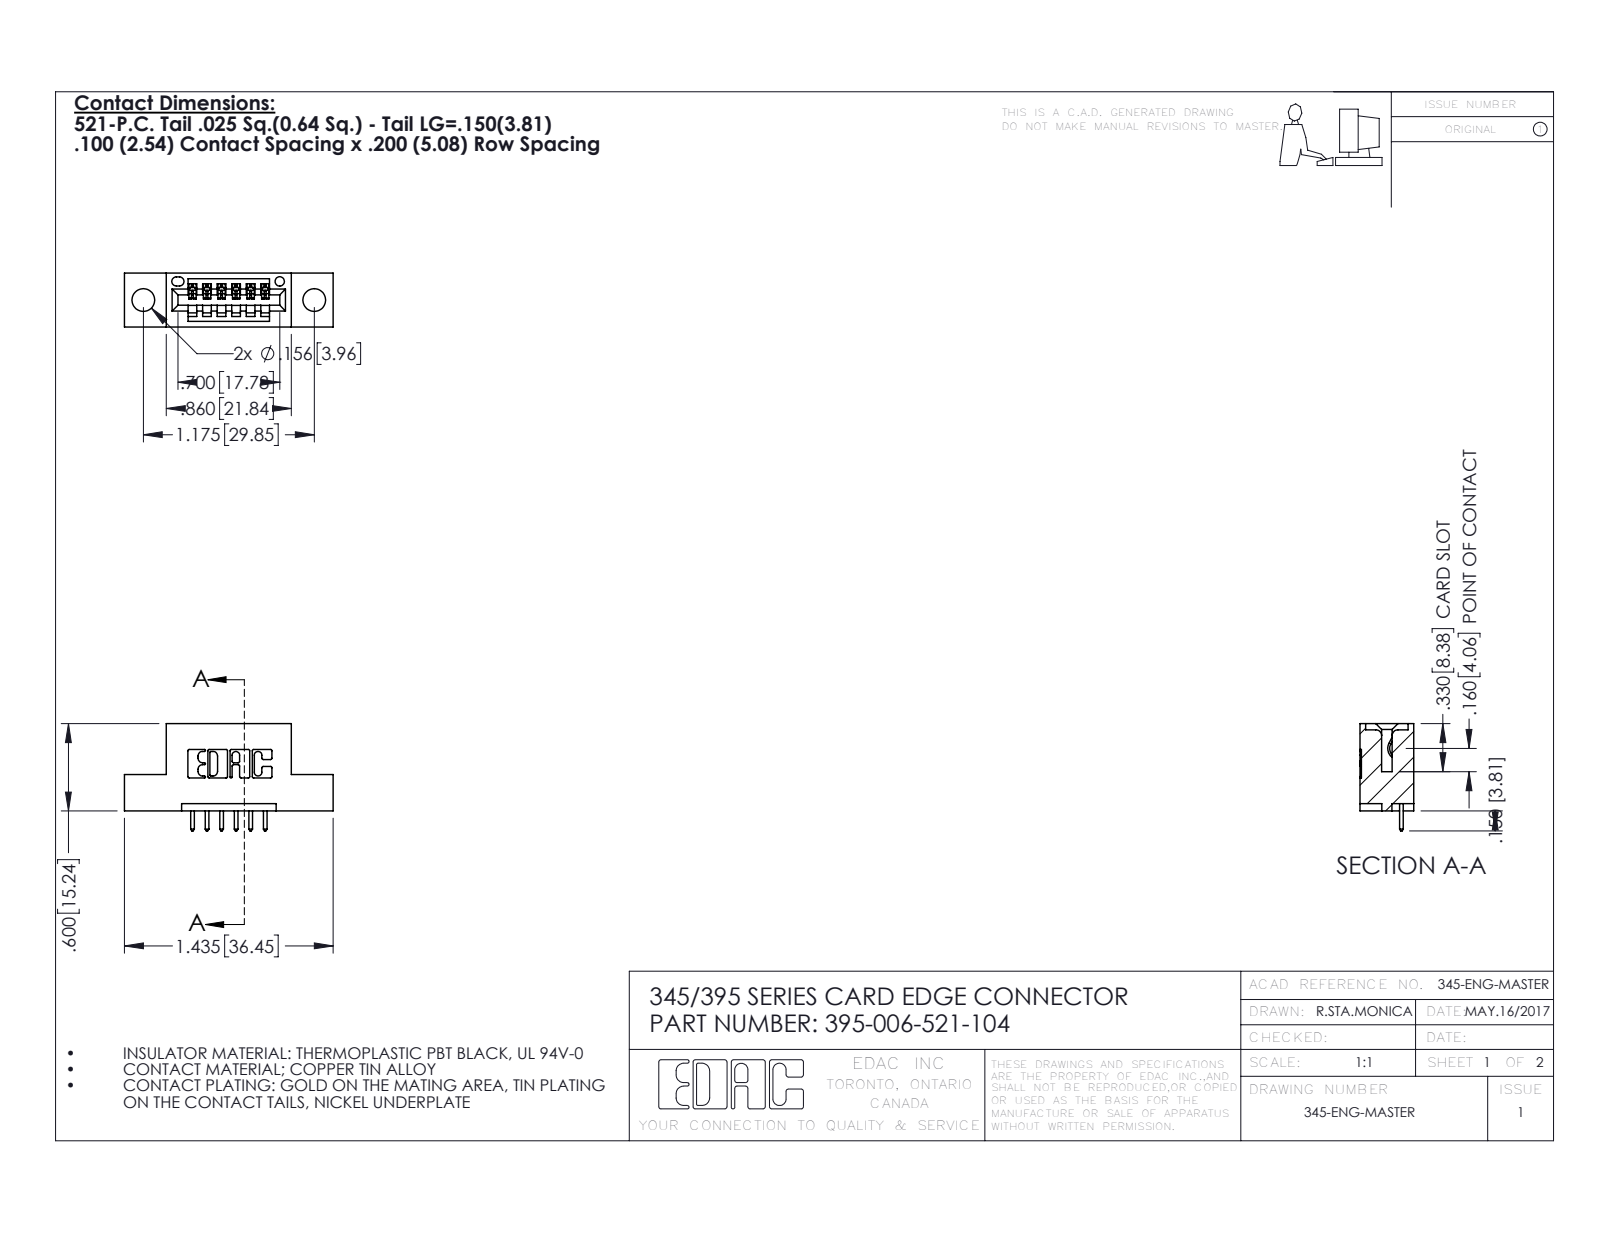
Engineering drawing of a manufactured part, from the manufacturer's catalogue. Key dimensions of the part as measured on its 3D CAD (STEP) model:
Part name (STEP PRODUCT): 395-006-521-104; 345-292-001_345-293-121; 345 Part_Flush Mounting Lugs - 0.156 Dia-TH
STEP written by: SolidWorks 2016 (CONFIG_CONTROL_DESIGN)
Units: inches
Bodies: 7 solids, 474 faces (320 planar, 154 cylindrical, 0 other)
Overall size (bounding box): 1.435 × 0.737 × 0.37
Volume: 0.187 in³ · Surface area: 5.149 in²
Round holes (diameter × count): ⌀0.156 ×2, ⌀0.064 ×1
Partial cylindrical surfaces — rounded edges, fillets, slot ends (radius × count): R0.01 ×22, R0.006 ×12, R0.01 ×12, R0.007 ×6, R0.031 ×6, R0.026 ×3, R0.031 ×2, R0.04 ×2
Main face-to-face distances: 0.2, 0.37, 0.298, 0.072, 0.1, 0.025, 0.098, 0.272, 0.06, 0.3
Hole centre spacings: 0.27, 0.946, 1.175
